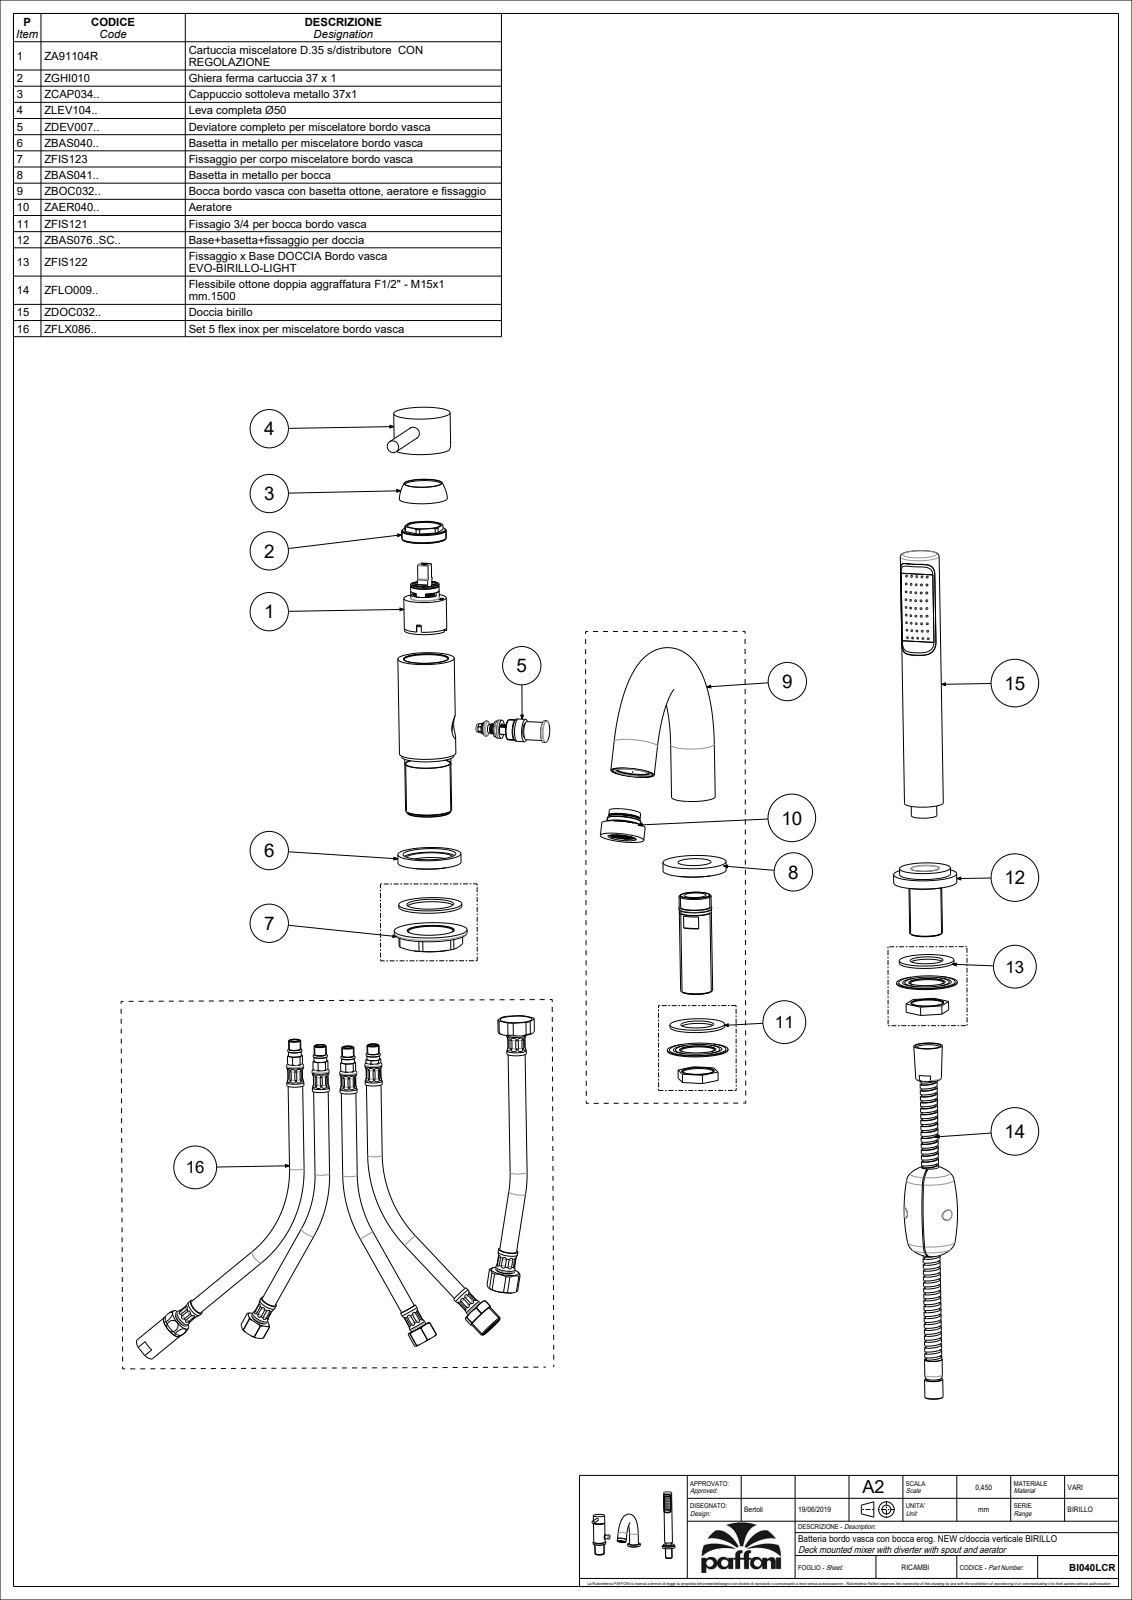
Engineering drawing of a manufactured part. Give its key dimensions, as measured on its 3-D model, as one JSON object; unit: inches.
{"part_name": "BI040LCR", "step_written_by": "CREO PARAMETRIC BY PTC INC, 2020044 (CONFIG_CONTROL_DESIGN)", "units": "inches", "bodies": {"solids": 6, "faces": 2058, "planar": 1196, "cylindrical": 623, "other": 239}, "overall_size": [13.858, 9.134, 8.103], "volume_in3": 19.04, "surface_area_in2": 308.3, "round_holes": [[0.02, 61], [0.059, 45], [0.276, 6], [1.937, 3], [0.157, 2], [0.748, 2], [1.055, 2], [1.071, 2], [1.299, 2], [1.339, 2], [0.122, 1], [0.13, 1]], "round_bosses_or_shafts": [[2.047, 3], [1.74, 3], [1.417, 2], [1.335, 2], [1.831, 1], [1.693, 1], [1.654, 1], [1.496, 1]], "partial_cylinders_radius": [[0.01, 30], [0.02, 27], [0.006, 11], [0.012, 4], [0.039, 2], [0.307, 2], [0.386, 2], [0.394, 2]], "face_to_face_distances": [0.276, 0.079, 0.197, 0.394, 0.472, 9.055, 0.787, 8.976, 0.098, 0.118], "hole_center_spacings": [0.226, 0.15, 0.311, 0.542, 0.075, 0.788, 0.256, 0.512]}
